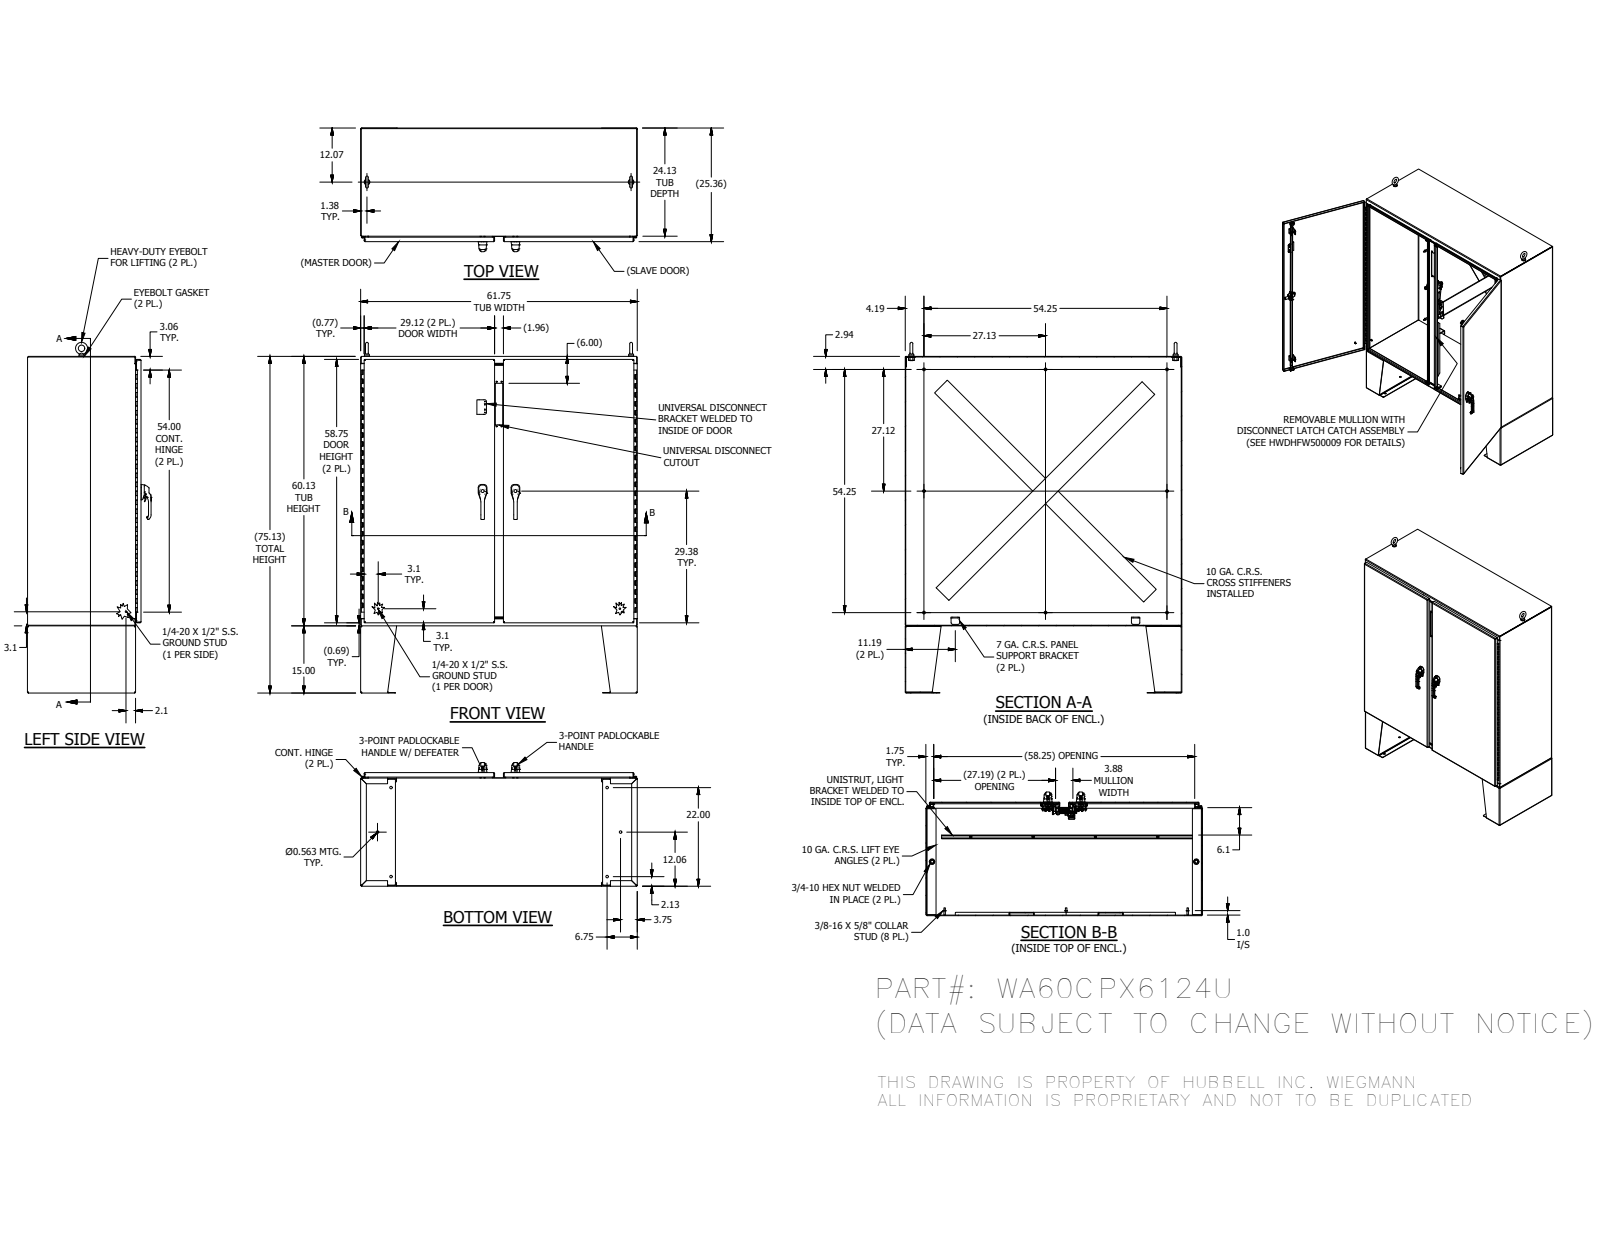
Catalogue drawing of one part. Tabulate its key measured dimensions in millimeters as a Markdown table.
| quantity | value |
| --- | --- |
| part name | WA60CPX6124UBLR; WACPX6124UTOP; WACPX6124UBTM; 30364 (+8 more) |
| STEP written by | Autodesk Inventor 2016 (AUTOMOTIVE_DESIGN) |
| units | millimeters |
| bodies | 210 solids, 8527 faces (3961 planar, 2849 cylindrical, 1717 other) |
| overall size | 1987.49 × 1568.45 × 701.25 |
| volume | 37 960 000 mm³ |
| surface area | 23 180 000 mm² |
| round holes (diameter × count) | 6.35 × 21, 9.52 × 18, 14.29 × 18, 5.08 × 8, 5.16 × 8, 7.02 × 8, 7.94 × 8, 3.96 × 6, 4.83 × 6, 4.98 × 6, 5.11 × 6, 5.4 × 6 |
| round bosses / shafts (diameter × count) | 6.35 × 19, 8.38 × 16, 15.88 × 14, 14.29 × 9, 9.52 × 9, 8.56 × 9, 25.4 × 8, 11.13 × 8 |
| partial cylindrical surfaces (radius × count) | 0.5 × 344, 0.3 × 202, 0.51 × 144, 0.47 × 42, 1.27 × 40, 3.17 × 40, 2.38 × 37, 2 × 27 |
| main face-to-face distances | 3.4, 640.5, 3.41, 637.1, 643.9, 1523.77, 1565.04, 3.18, 1520.36, 1561.64 |
| hole center spacings | 27.99, 186.28, 70.08, 187.63, 22.5, 29, 30.36, 32.29 |
